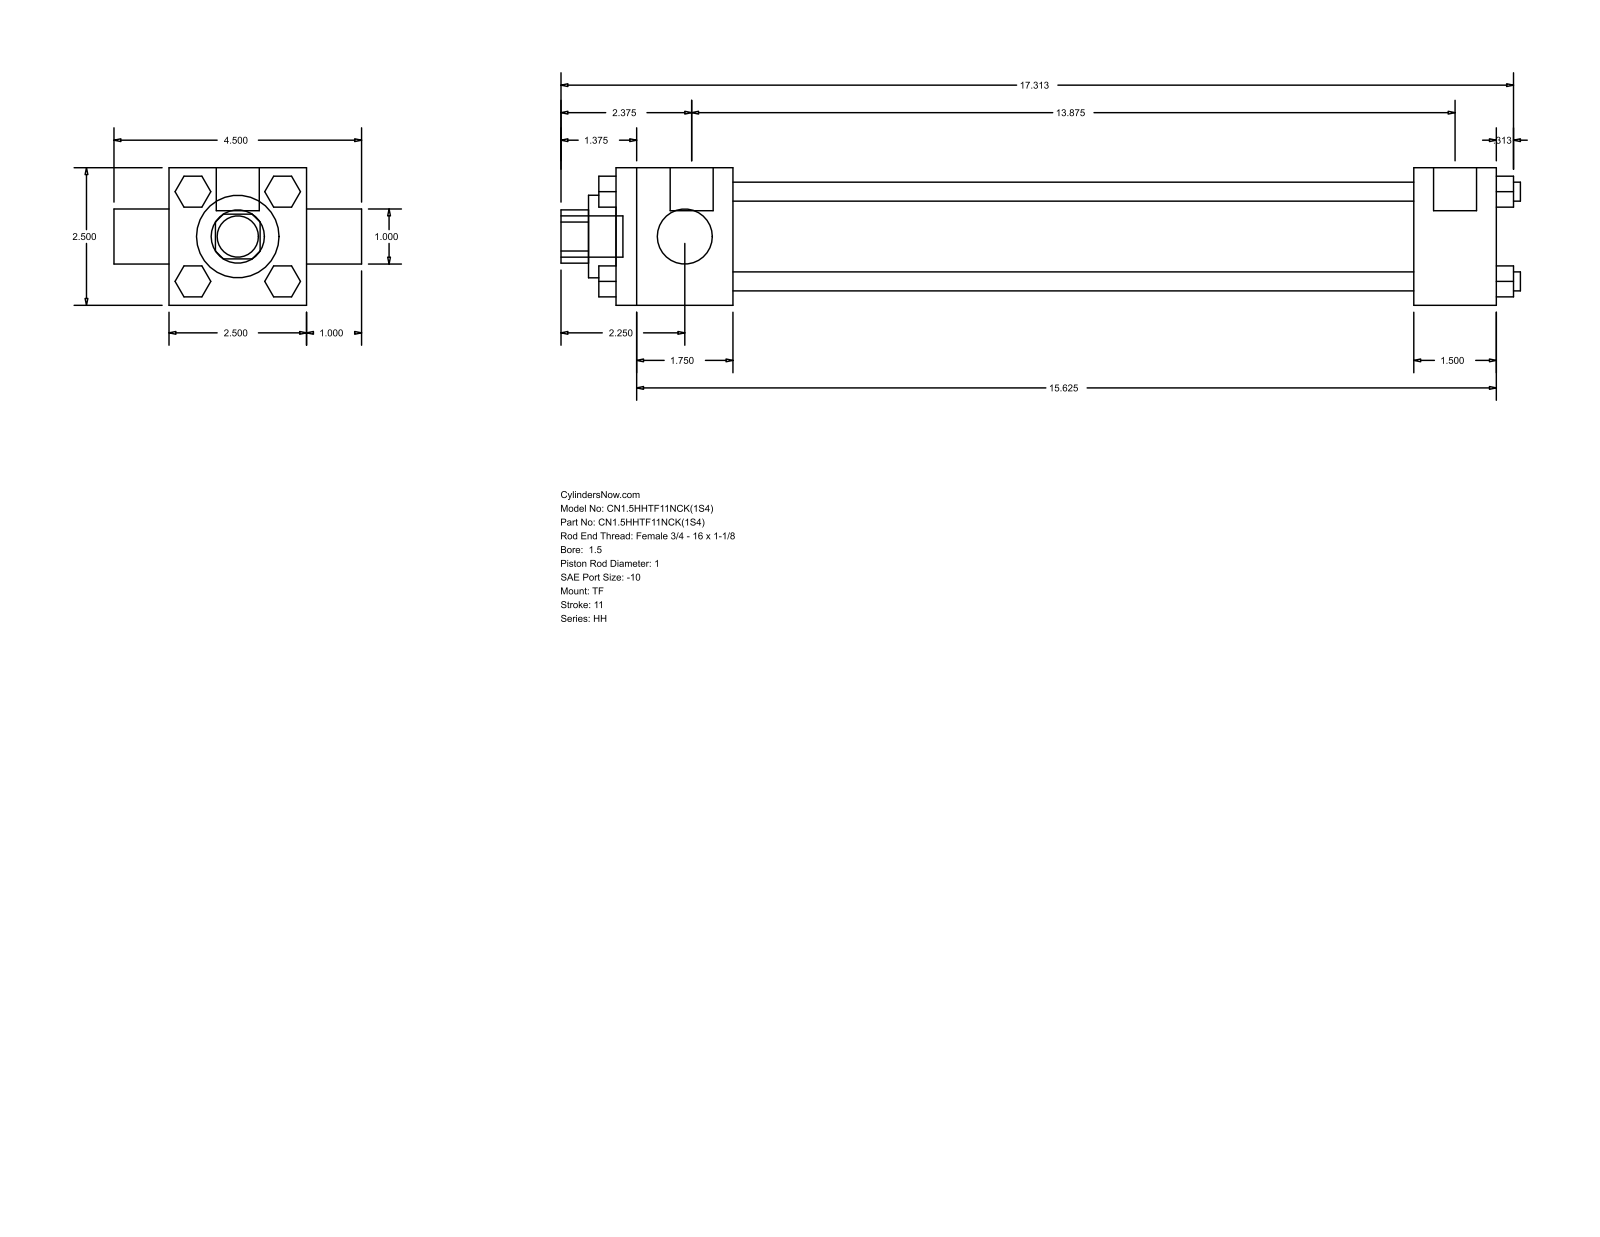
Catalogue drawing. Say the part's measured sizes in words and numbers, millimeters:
The part is named "HH_TF__0150_1". Its 3-D file was written by "GSSL Pune (CONFIG_CONTROL_DESIGN)". It is 0 solids with 120 faces: 92 planar, 28 cylindrical and 0 other. Overall it measures 442.91 by 114.3 by 63.5 millimeters. Round holes: 2 of diameter 25.4, 1 of diameter 38.1, 1 of diameter 44.45. Round bosses or shafts: 4 of diameter 8.76, 3 of diameter 5.56, 2 of diameter 19.84, 1 of diameter 19.05. Partial cylindrical surfaces (rounded edges, fillets, slot ends): 1 of radius 12.29. The main face-to-face distances are 63.5, 352.42, 314.32, 38.1, 53.98, 368.3, 406.4, 414.34, 25.4, 20.7.
